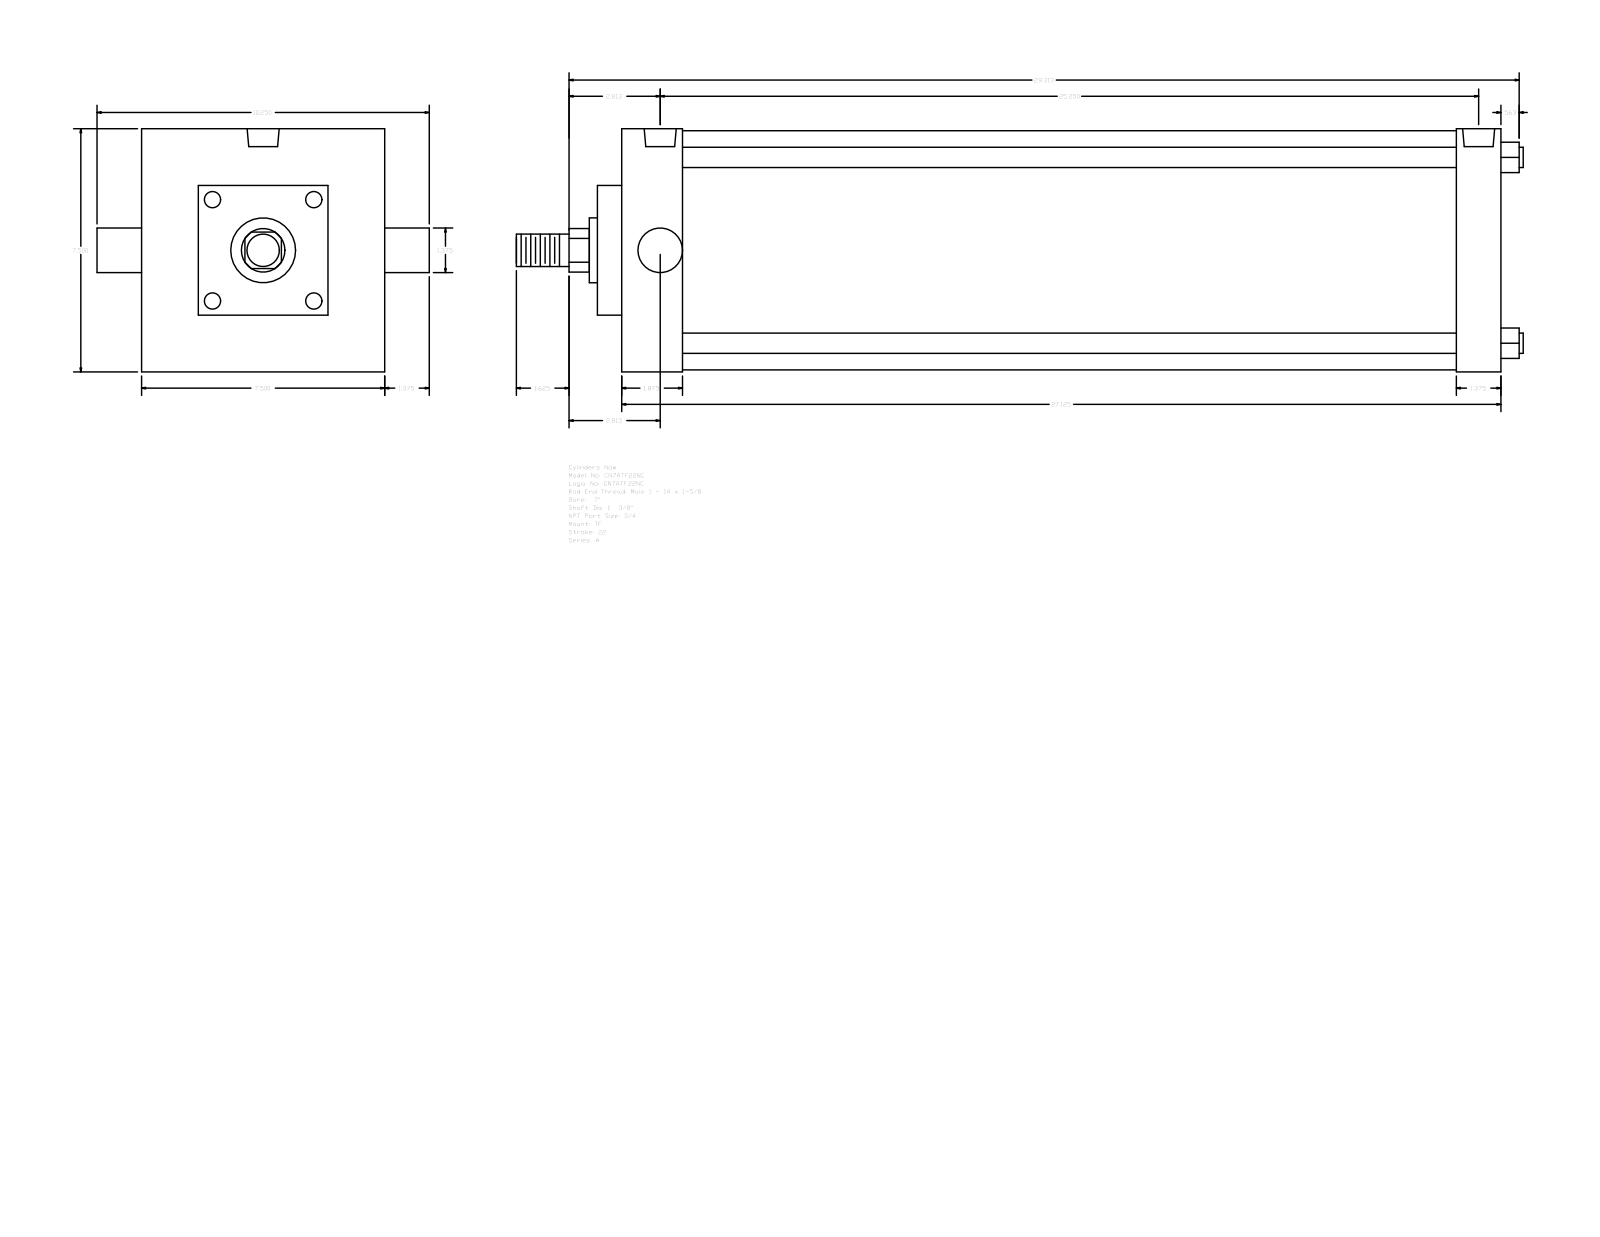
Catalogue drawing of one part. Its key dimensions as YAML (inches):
part_name: "A_TF__0700_1.375"
step_written_by: "GSSL Pune (CONFIG_CONTROL_DESIGN)"
units: inches
bodies: {solids: 0, faces: 89, planar: 65, cylindrical: 24, other: 0}
overall_size: [31.063, 10.25, 7.5]
round_holes:
  - {diameter: 0.594, count: 3}
  - {diameter: 0.989, count: 2}
round_bosses_or_shafts:
  - {diameter: 0.625, count: 4}
  - {diameter: 1.375, count: 2}
  - {diameter: 7.375, count: 1}
  - {diameter: 2, count: 1}
  - {diameter: 1, count: 1}
partial_cylinders:
  - {radius: 0.672, count: 1}
face_to_face_distances: [7.5, 27.125, 0.75, 27.875, 2.625, 1.875, 25.25, 26.5, 25.75, 23.875]
hole_center_spacings: [0.219, 25.031, 24.812, 25.25]
